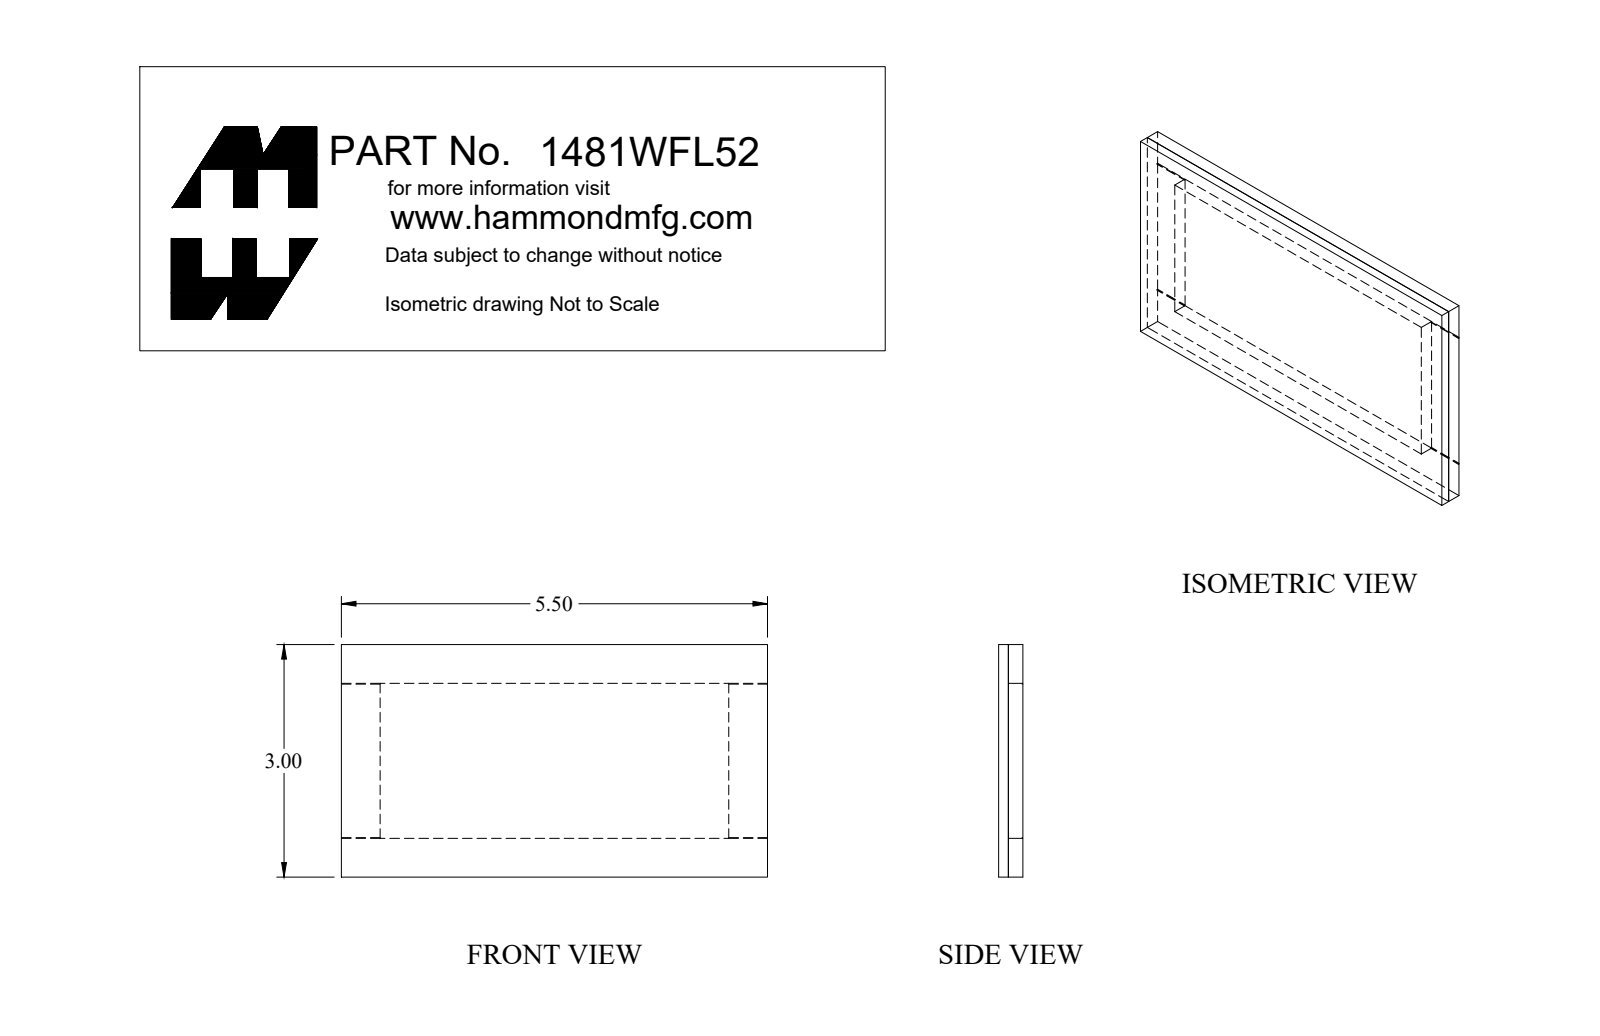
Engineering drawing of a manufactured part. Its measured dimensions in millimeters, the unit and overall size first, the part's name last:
Units: millimetres
Overall size (bounding box): 139.7 × 76.2 × 8
Main face-to-face distances: 3.2, 8, 4.7, 12.7, 76.2, 63.5, 139.7, 50.8, 127, 114.3
Volume: 56 850 mm³ · Surface area: 35 990 mm²
Bodies: 2 solids, 27 faces (27 planar, 0 cylindrical, 0 other)
Part name (STEP PRODUCT): 1481WFL52_Default
STEP written by: SolidWorks 2019 (CONFIG_CONTROL_DESIGN)
